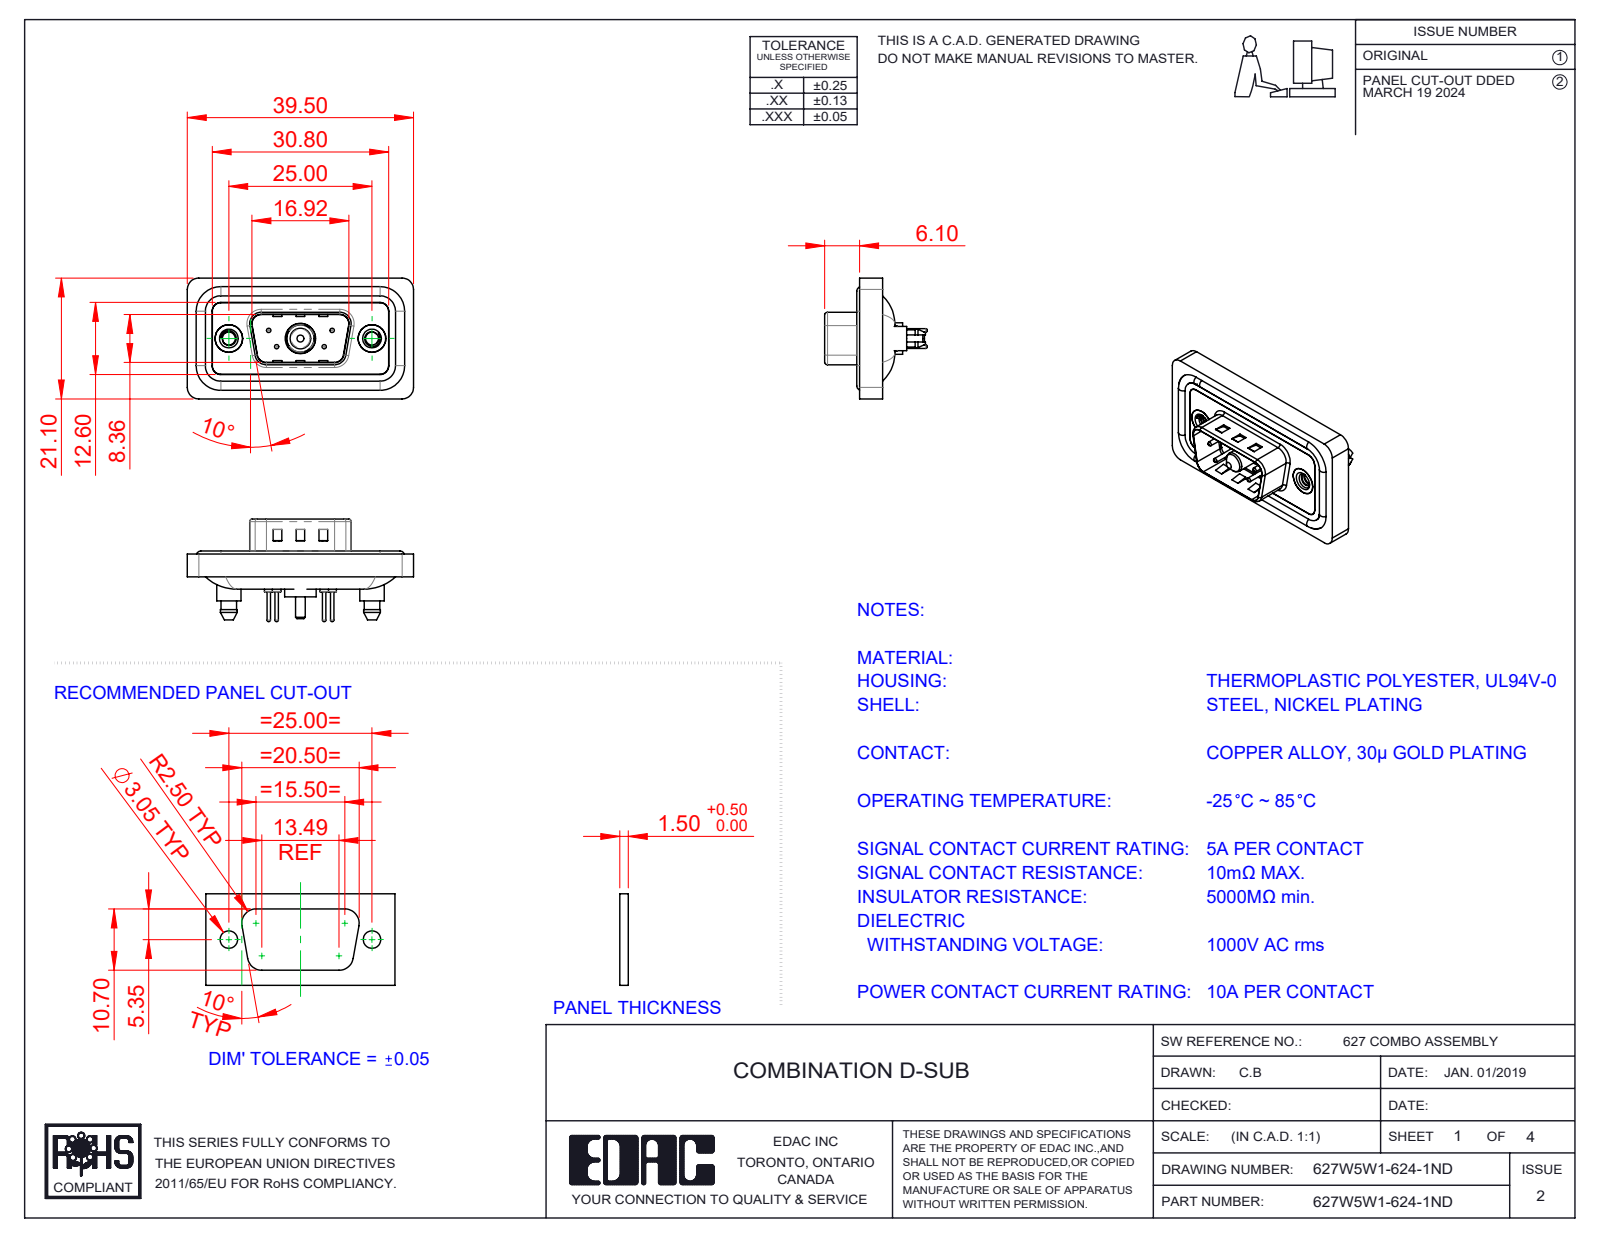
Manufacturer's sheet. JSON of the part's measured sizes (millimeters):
{"part_name": "627Combo Housing_5W1; 627W5W1-624-1ND; 627Combo Shell Rear_09 Contacts; 627Combo Contact Row 1_24 (+6 more)", "step_written_by": "SolidWorks 2023 (CONFIG_CONTROL_DESIGN)", "units": "millimeters", "bodies": {"solids": 13, "faces": 656, "planar": 199, "cylindrical": 295, "other": 162}, "overall_size": [39.5, 21.1, 17.9], "volume_mm3": 4507, "surface_area_mm2": 7265, "round_holes": [[0.75, 4], [1.6, 4], [2, 4], [2.26, 2], [4, 2], [4.8, 2], [5, 2], [4.85, 1], [5.3, 1]], "round_bosses_or_shafts": [[1.6, 4], [1.5, 4], [0.6, 4], [5.4, 2], [4.9, 2], [4.25, 2], [5.5, 1], [5.2, 1]], "partial_cylinders_radius": [[1.5, 24], [2, 18], [1.6, 10], [0.5, 8], [0.25, 4], [0.6, 4], [0.65, 4], [0.9, 4]], "face_to_face_distances": [0.4, 1.1, 2.9, 1.6, 1.5, 3.1, 0.5, 2.5, 4, 0.7], "hole_center_spacings": [3.16, 5.72, 7.1, 12.5, 18.1, 4.39, 4.4, 8.31]}
